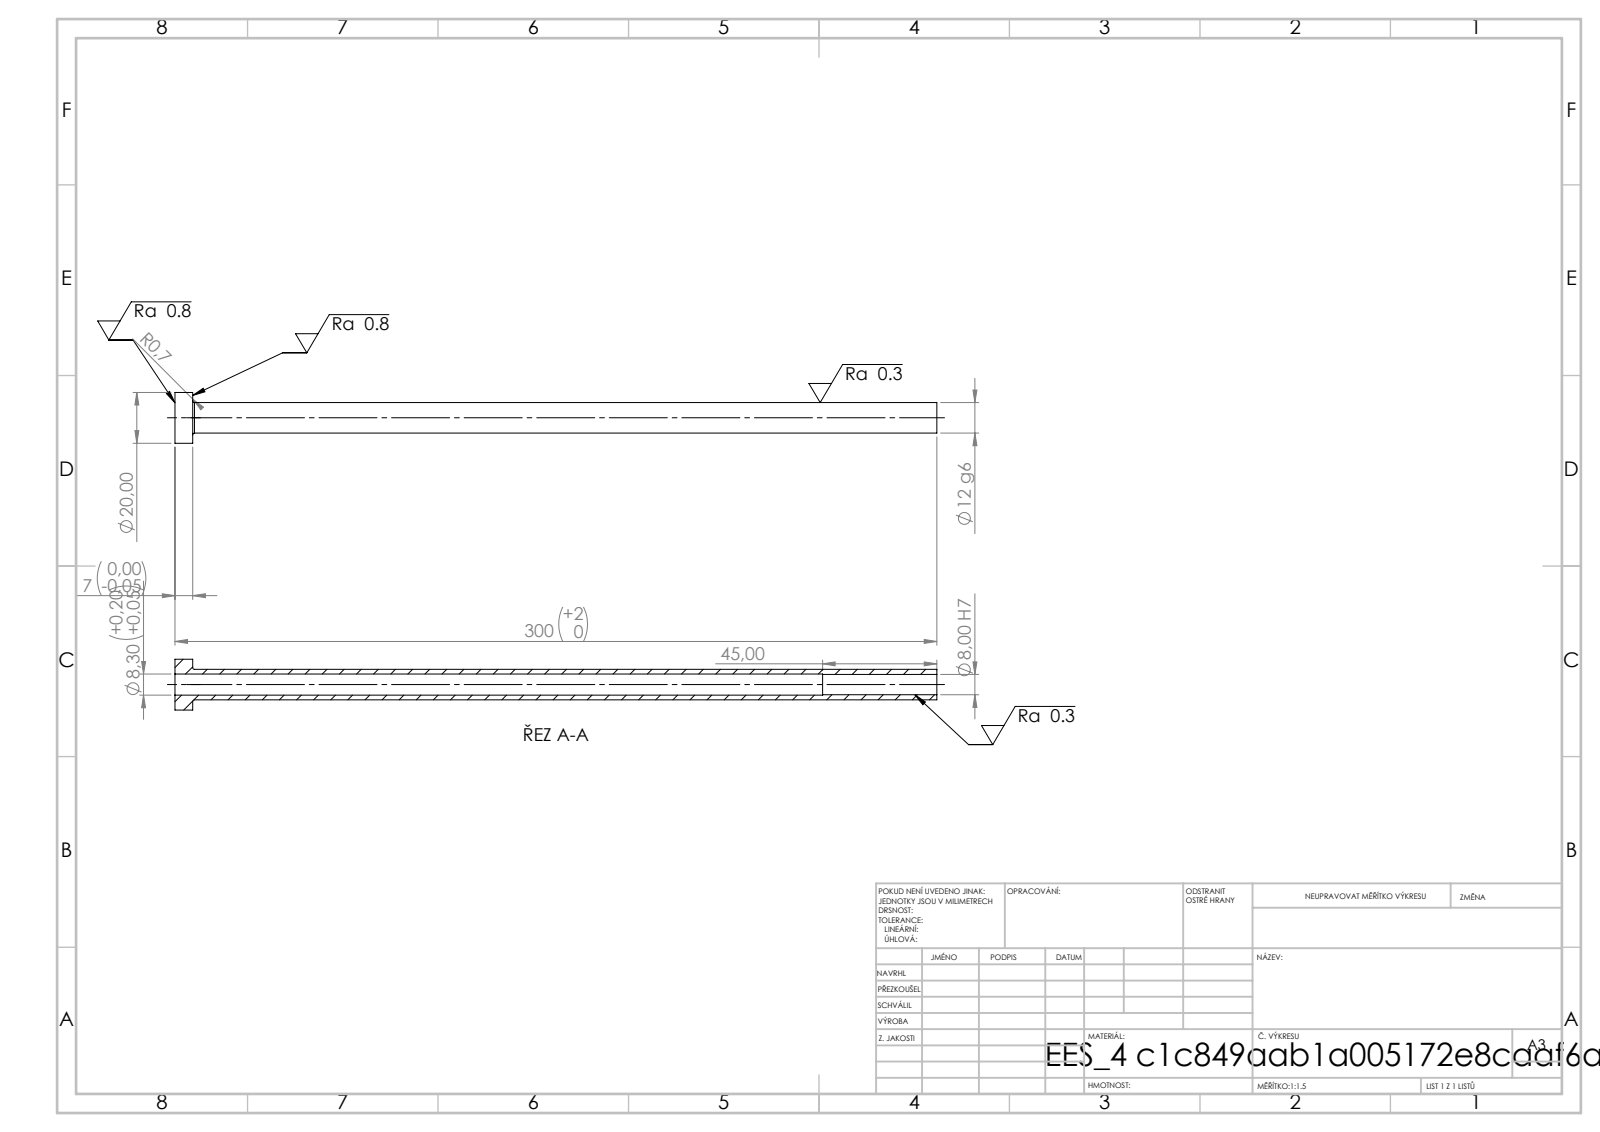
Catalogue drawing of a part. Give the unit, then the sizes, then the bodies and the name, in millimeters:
Units: millimetres
Overall size (bounding box): 300 × 20 × 20
Round holes (diameter × count): ⌀8 ×1, ⌀8.3 ×1
Round bosses / shafts (diameter × count): ⌀20 ×1, ⌀12 ×1
Main face-to-face distances: 7, 300, 293, 255, 248, 45
Volume: 19 282 mm³ · Surface area: 19 782 mm²
Bodies: 1 solid, 14 faces (4 planar, 8 cylindrical, 2 other)
STEP written by: SolidWorks 2019 (CONFIG_CONTROL_DESIGN)
